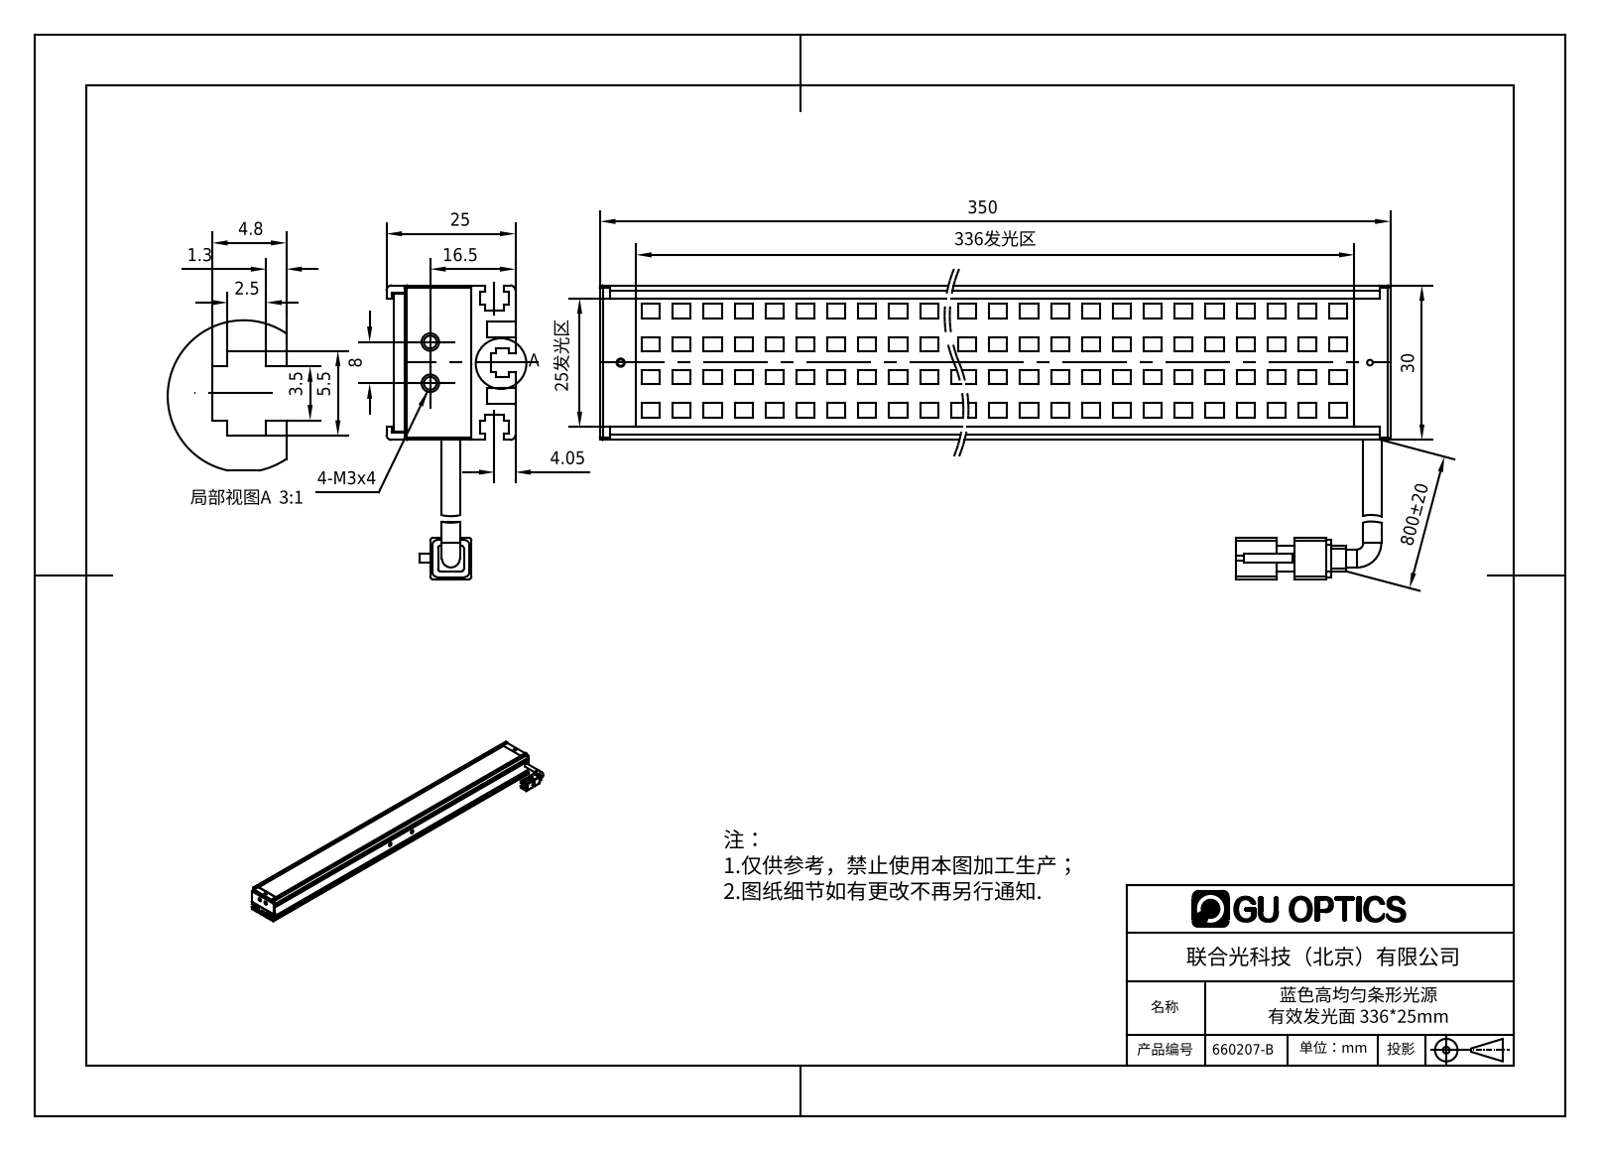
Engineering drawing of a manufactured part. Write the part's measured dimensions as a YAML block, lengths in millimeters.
part_name: "660207-B"
step_written_by: "SolidWorks 2016 (AUTOMOTIVE_DESIGN)"
units: millimeters
bodies: {solids: 6, faces: 1564, planar: 1378, cylindrical: 83, other: 103}
overall_size: [350, 57, 25]
volume: 118035
surface_area: 120531
round_holes:
  - {diameter: 1.6, count: 5}
  - {diameter: 1.5, count: 2}
  - {diameter: 1.7, count: 2}
  - {diameter: 2.5, count: 2}
  - {diameter: 2.8, count: 2}
  - {diameter: 3, count: 2}
  - {diameter: 1.1, count: 1}
  - {diameter: 1.25, count: 1}
  - {diameter: 2, count: 1}
round_bosses_or_shafts:
  - {diameter: 3.5, count: 2}
partial_cylinders:
  - {radius: 1, count: 12}
  - {radius: 0.5, count: 8}
  - {radius: 1.65, count: 1}
face_to_face_distances: [1, 13, 2, 2.5, 3, 27.5, 9.5, 4.5, 12, 15.1]
hole_center_spacings: [342, 7, 156, 156.14, 186, 186.12, 342.07, 8]
